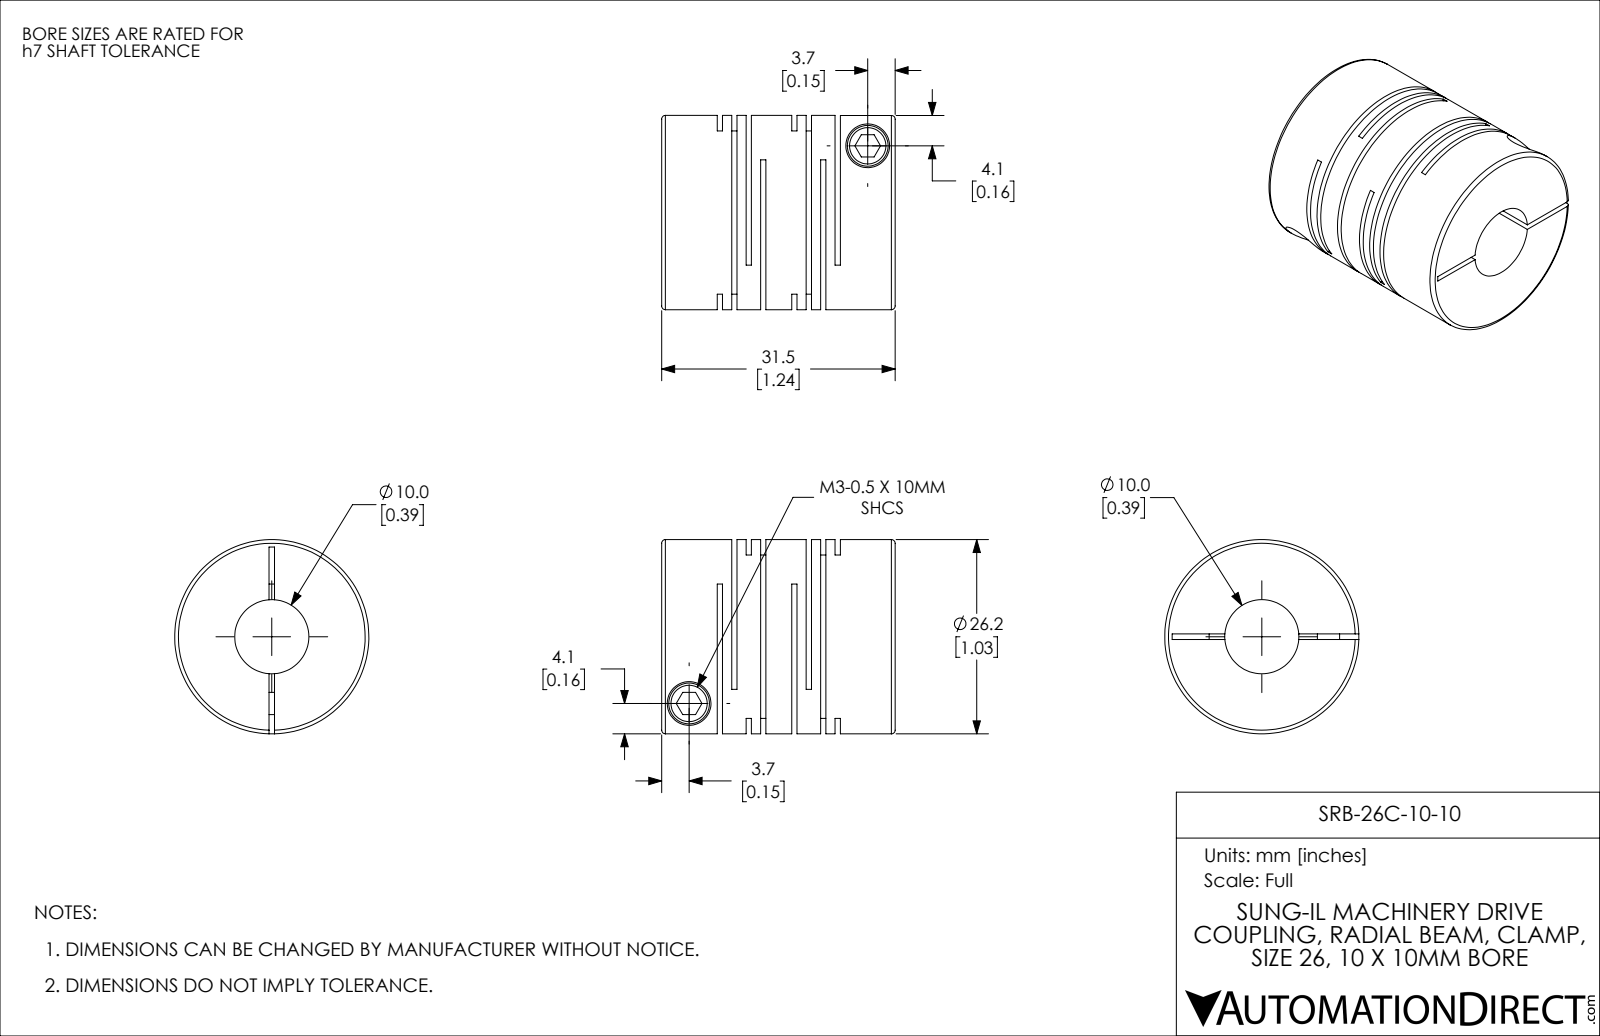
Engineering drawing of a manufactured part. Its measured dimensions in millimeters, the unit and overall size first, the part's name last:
Units: millimetres
Overall size (bounding box): 31.5 × 26.2 × 26.2
Round holes (diameter × count): ⌀3 ×2, ⌀5.9 ×2, ⌀10 ×1
Round bosses / shafts (diameter × count): ⌀5.5 ×2, ⌀26.2 ×1
Main face-to-face distances: 1.95, 10.05, 0.71, 3.9, 8.1, 12, 1.24, 2.66, 9.34, 13.95
Volume: 11 943 mm³ · Surface area: 10 725 mm²
Bodies: 1 solid, 114 faces (60 planar, 42 cylindrical, 12 other)
Part name (STEP PRODUCT): SRB-26C-10-10
STEP written by: SolidWorks 2021 (CONFIG_CONTROL_DESIGN)
